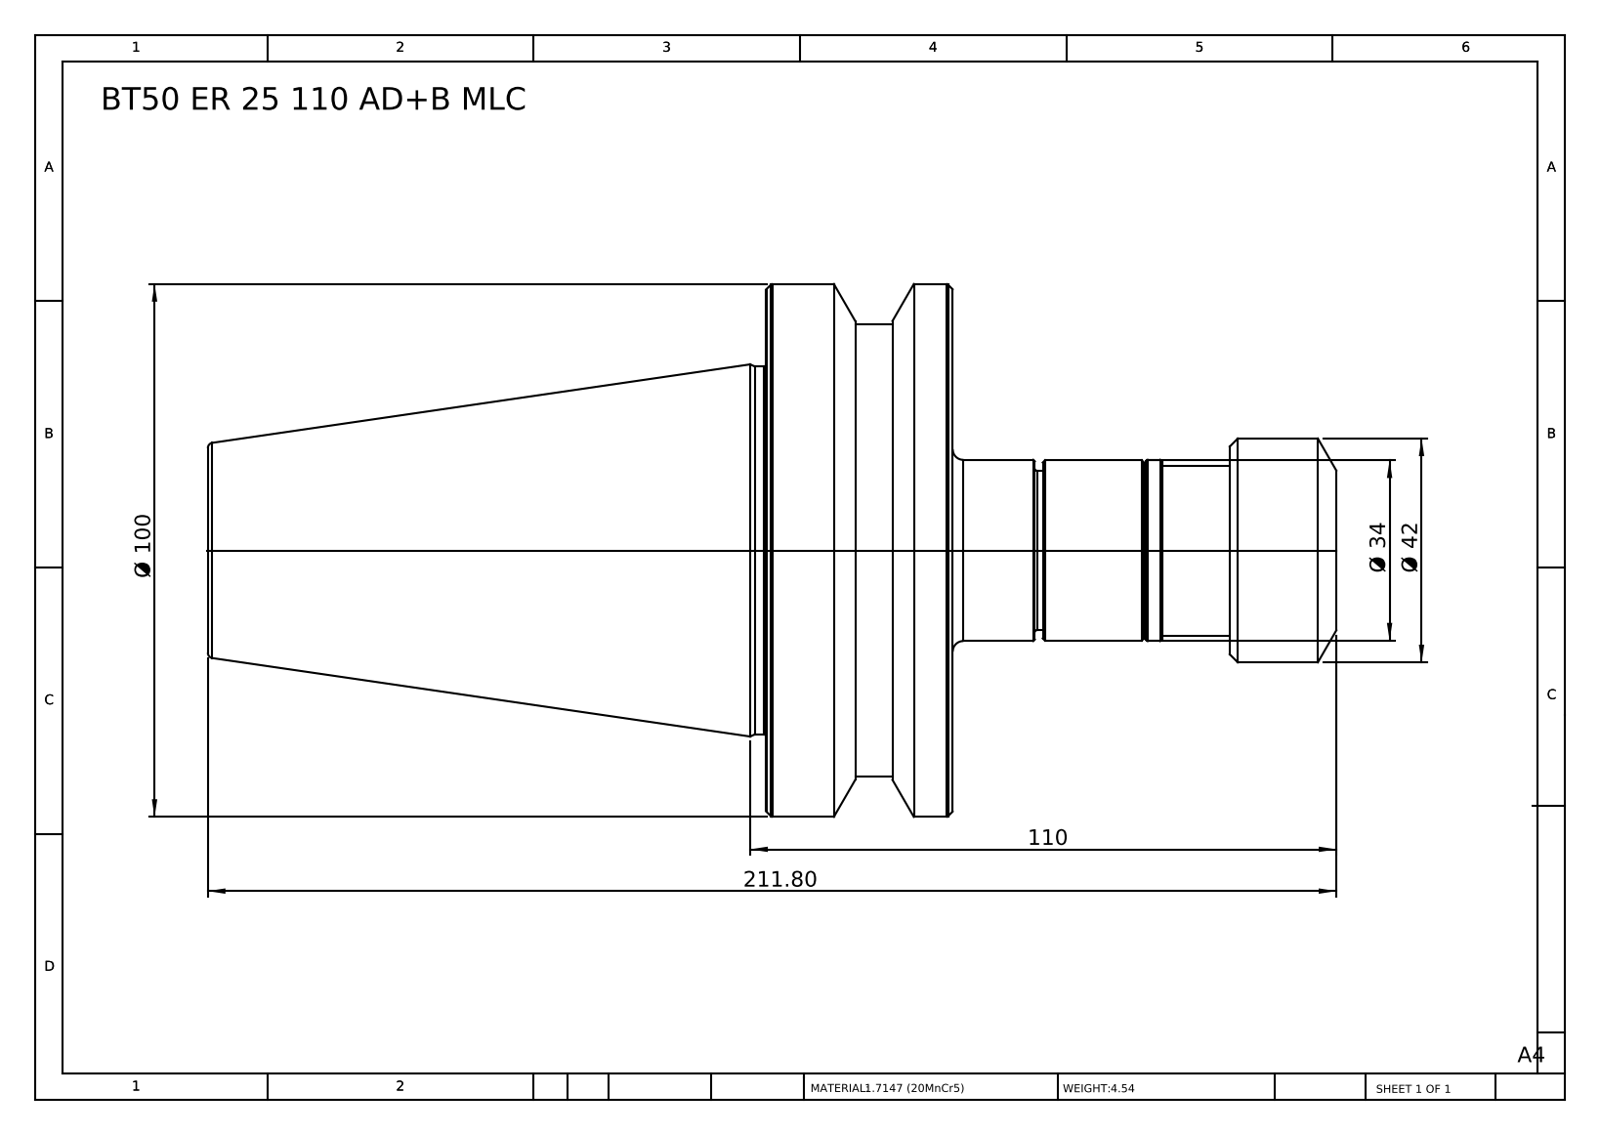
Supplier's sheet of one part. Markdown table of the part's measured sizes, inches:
| quantity | value |
| --- | --- |
| part name | BT50 ER 25 110 AD+B MLC |
| STEP written by | SolidWorks 2014 (CONFIG_CONTROL_DESIGN) |
| units | inches |
| bodies | 1 solid, 76 faces (12 planar, 22 cylindrical, 42 other) |
| overall size | 8.339 × 3.937 × 3.937 |
| volume | 35.5 in³ |
| surface area | 83.24 in² |
| round bosses / shafts (diameter × count) | 3.937 × 1, 3.346 × 1, 2.717 × 1, 1.654 × 1, 1.339 × 1, 1.331 × 1, 1.256 × 1, 1.177 × 1 |
| main face-to-face distances | 1.378, 5.504, 4.126, 2.835, 4.213, 8.339, 0.787, 2.047, 3.425, 7.551 |
